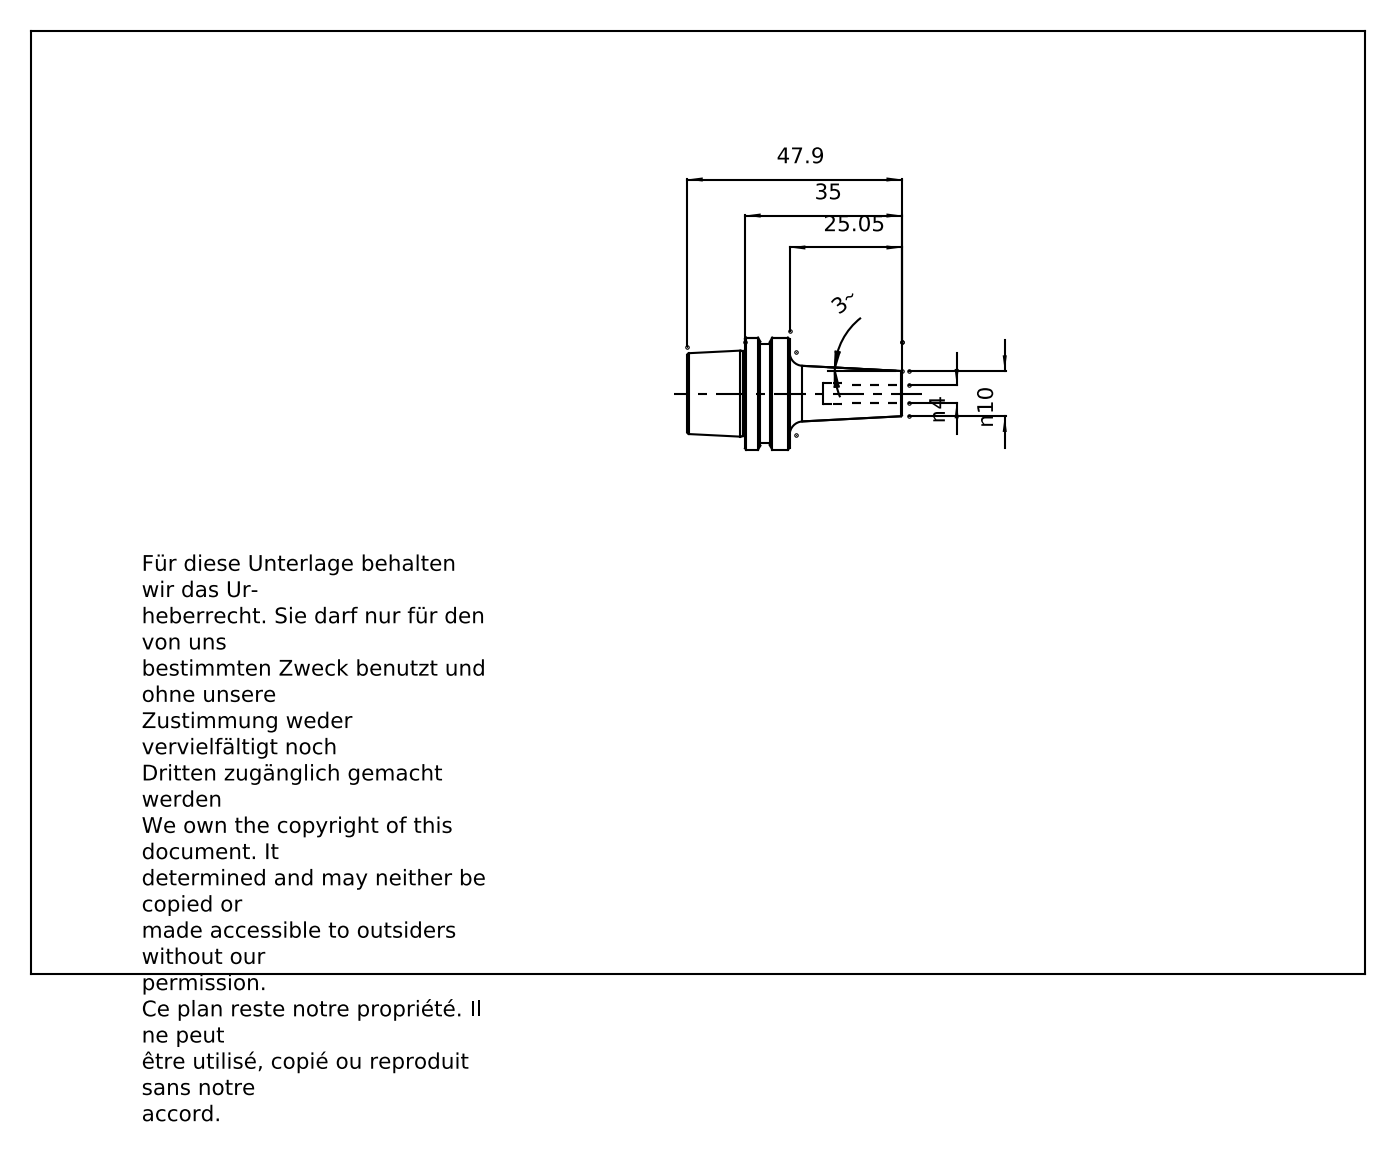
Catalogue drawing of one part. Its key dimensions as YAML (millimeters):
part_name: "E25-185-04"
step_written_by: "PRO/ENGINEER BY PARAMETRIC TECHNOLOGY CORPORATION, 2010430 (CONFIG_CONTROL_DESIGN)"
units: millimeters
bodies: {solids: 1, faces: 60, planar: 8, cylindrical: 16, other: 36}
overall_size: [47.9, 25, 25]
volume: 7178
surface_area: 4554
round_holes:
  - {diameter: 4, count: 1}
  - {diameter: 14.04, count: 1}
  - {diameter: 16.45, count: 1}
round_bosses_or_shafts:
  - {diameter: 25, count: 1}
  - {diameter: 21.95, count: 1}
  - {diameter: 18.96, count: 1}
face_to_face_distances: [4, 5.95, 9.95, 35, 29.05, 25.05, 12.9, 18.85, 22.85, 47.9]
